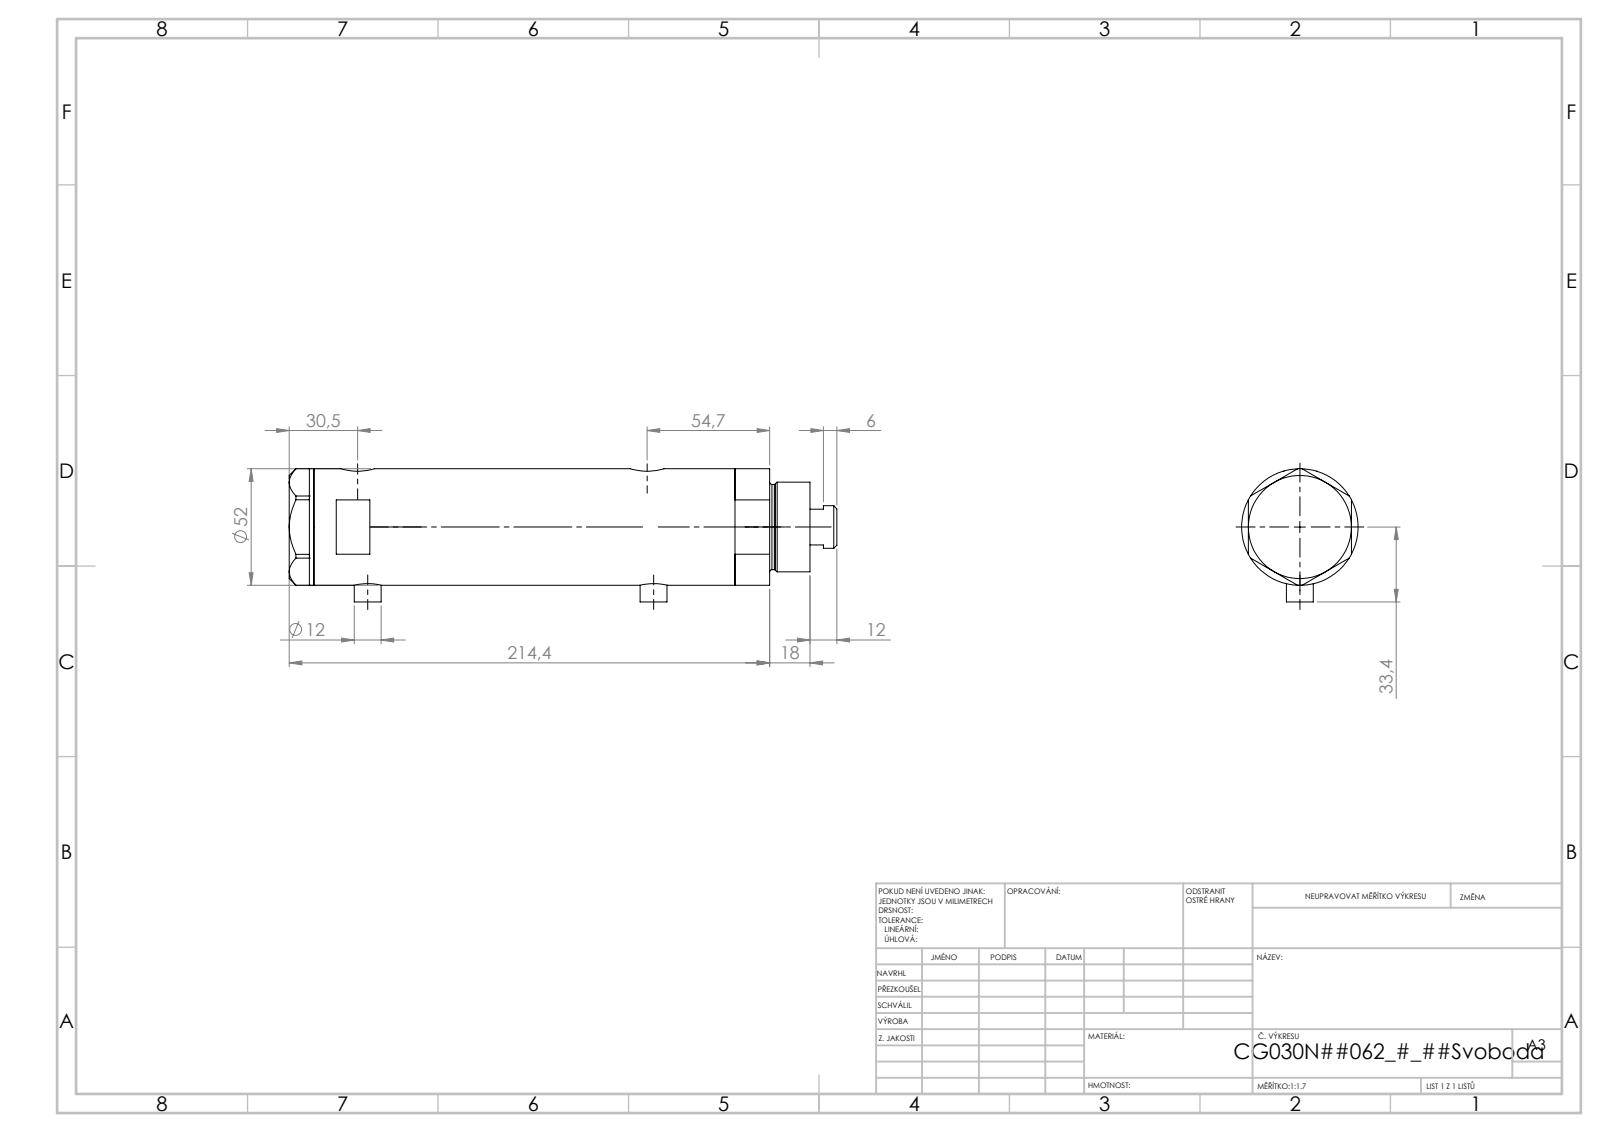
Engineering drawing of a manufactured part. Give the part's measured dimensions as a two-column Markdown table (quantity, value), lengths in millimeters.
| quantity | value |
| --- | --- |
| part name | V270CG_FRONT; V270CG_VC; V270CG_BACK; V270CG_MIDDLE |
| STEP written by | SolidWorks 2019 (CONFIG_CONTROL_DESIGN) |
| units | millimeters |
| bodies | 4 solids, 140 faces (67 planar, 53 cylindrical, 20 other) |
| overall size | 244.4 × 59.4 × 52 |
| volume | 448 128 mm³ |
| surface area | 97 552 mm² |
| round holes (diameter × count) | 5 × 2, 9.73 × 2, 12.5 × 2, 15 × 2, 6.5 × 1, 20 × 1, 21.5 × 1, 30 × 1, 33 × 1, 44 × 1 |
| round bosses / shafts (diameter × count) | 12 × 2, 52 × 1, 40 × 1, 38 × 1, 19 × 1 |
| main face-to-face distances | 151.5, 23.8, 127.7, 11, 34.8, 162.5, 46, 198.9, 187.9, 164.1 |
| hole center spacings | 2.9, 4.5, 124.7, 127.6, 129.2, 132.1 |
